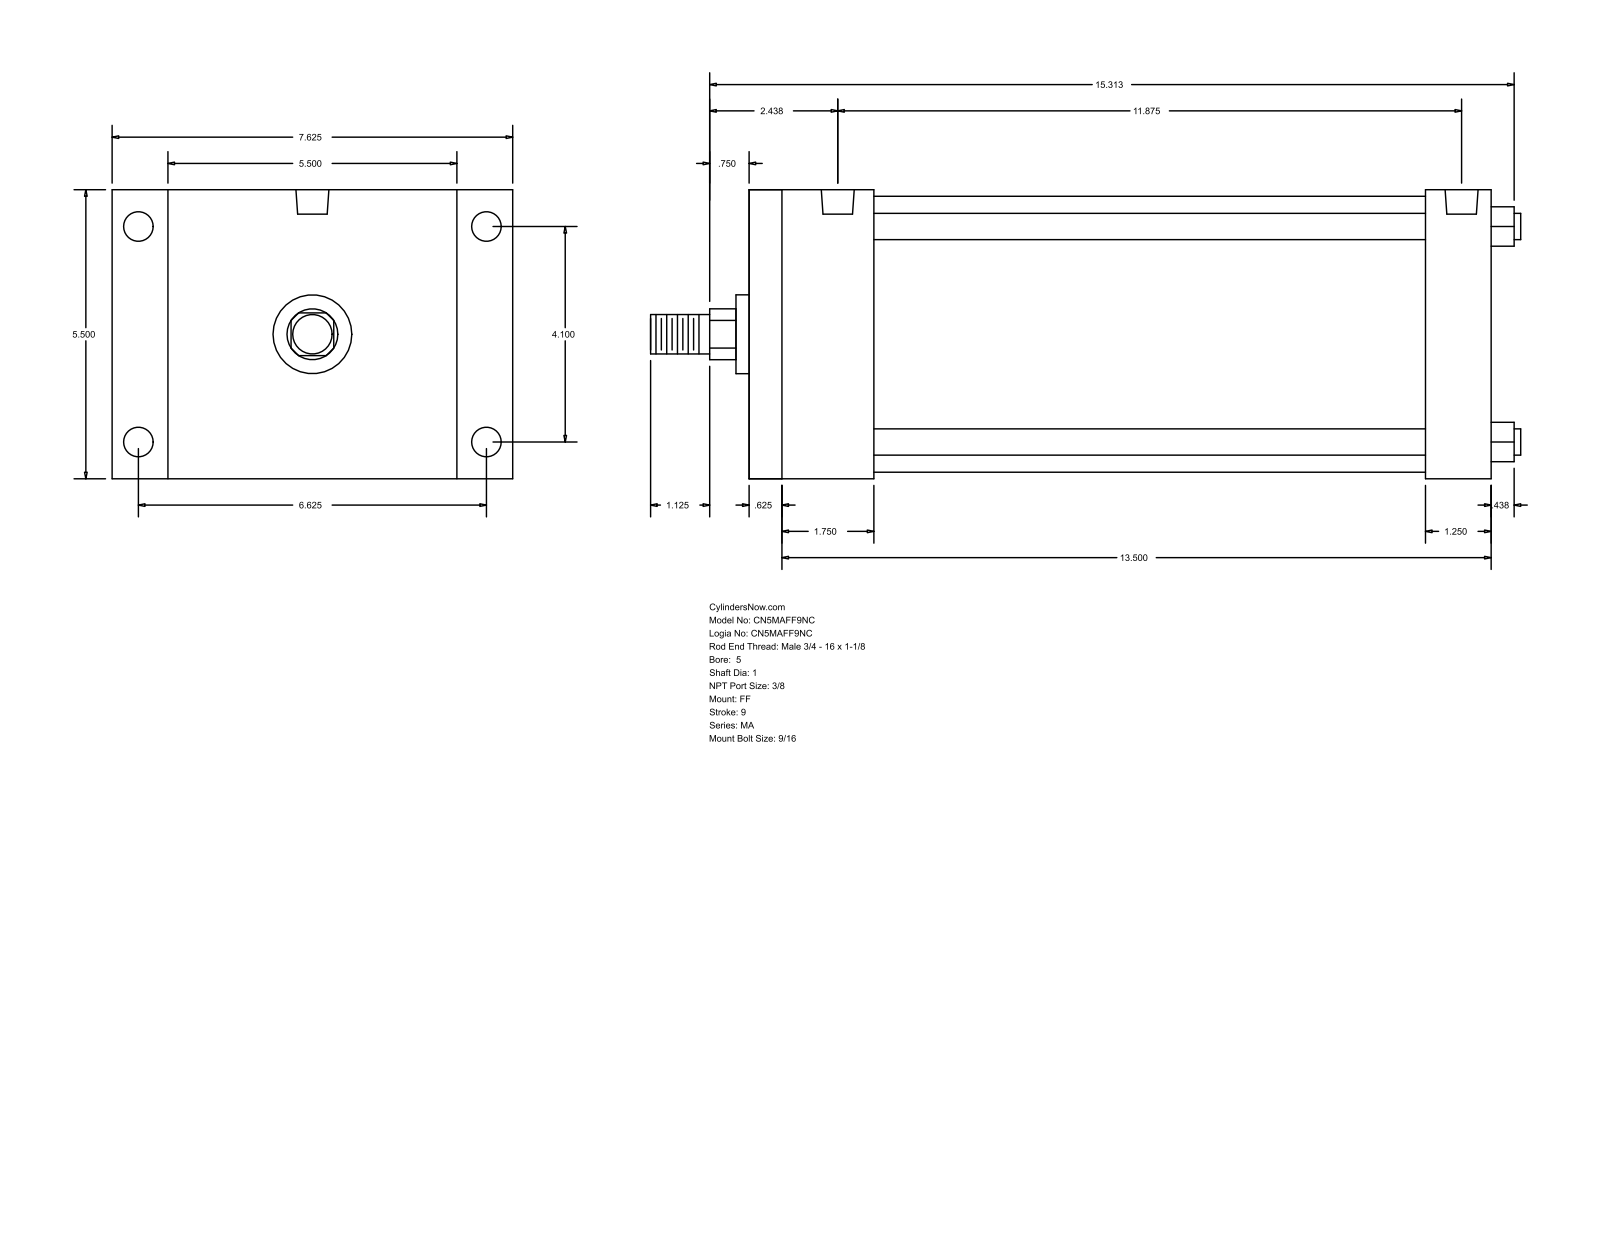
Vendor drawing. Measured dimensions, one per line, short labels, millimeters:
name: MA_FF__0500_1
written by: GSSL Pune (CONFIG_CONTROL_DESIGN)
unit: mm
bodies: 0 solids, 92 faces (64 planar, 28 cylindrical, 0 other)
size: 420.69 × 193.68 × 139.7
holes: 4× ⌀11.11, 4× ⌀14.29, 2× ⌀15.93
bosses: 4× ⌀12.7, 1× ⌀133.35, 1× ⌀38.1, 1× ⌀25.4, 1× ⌀19.05
rounds: 1× R12.29
face distances: 139.7, 358.77, 15.87, 342.9, 327.02, 311.15, 31.75, 60.33, 44.46, 266.69
hole spacings: 104.14, 168.28, 197.9, 292.1, 4.76, 4.77, 296.86, 296.87
